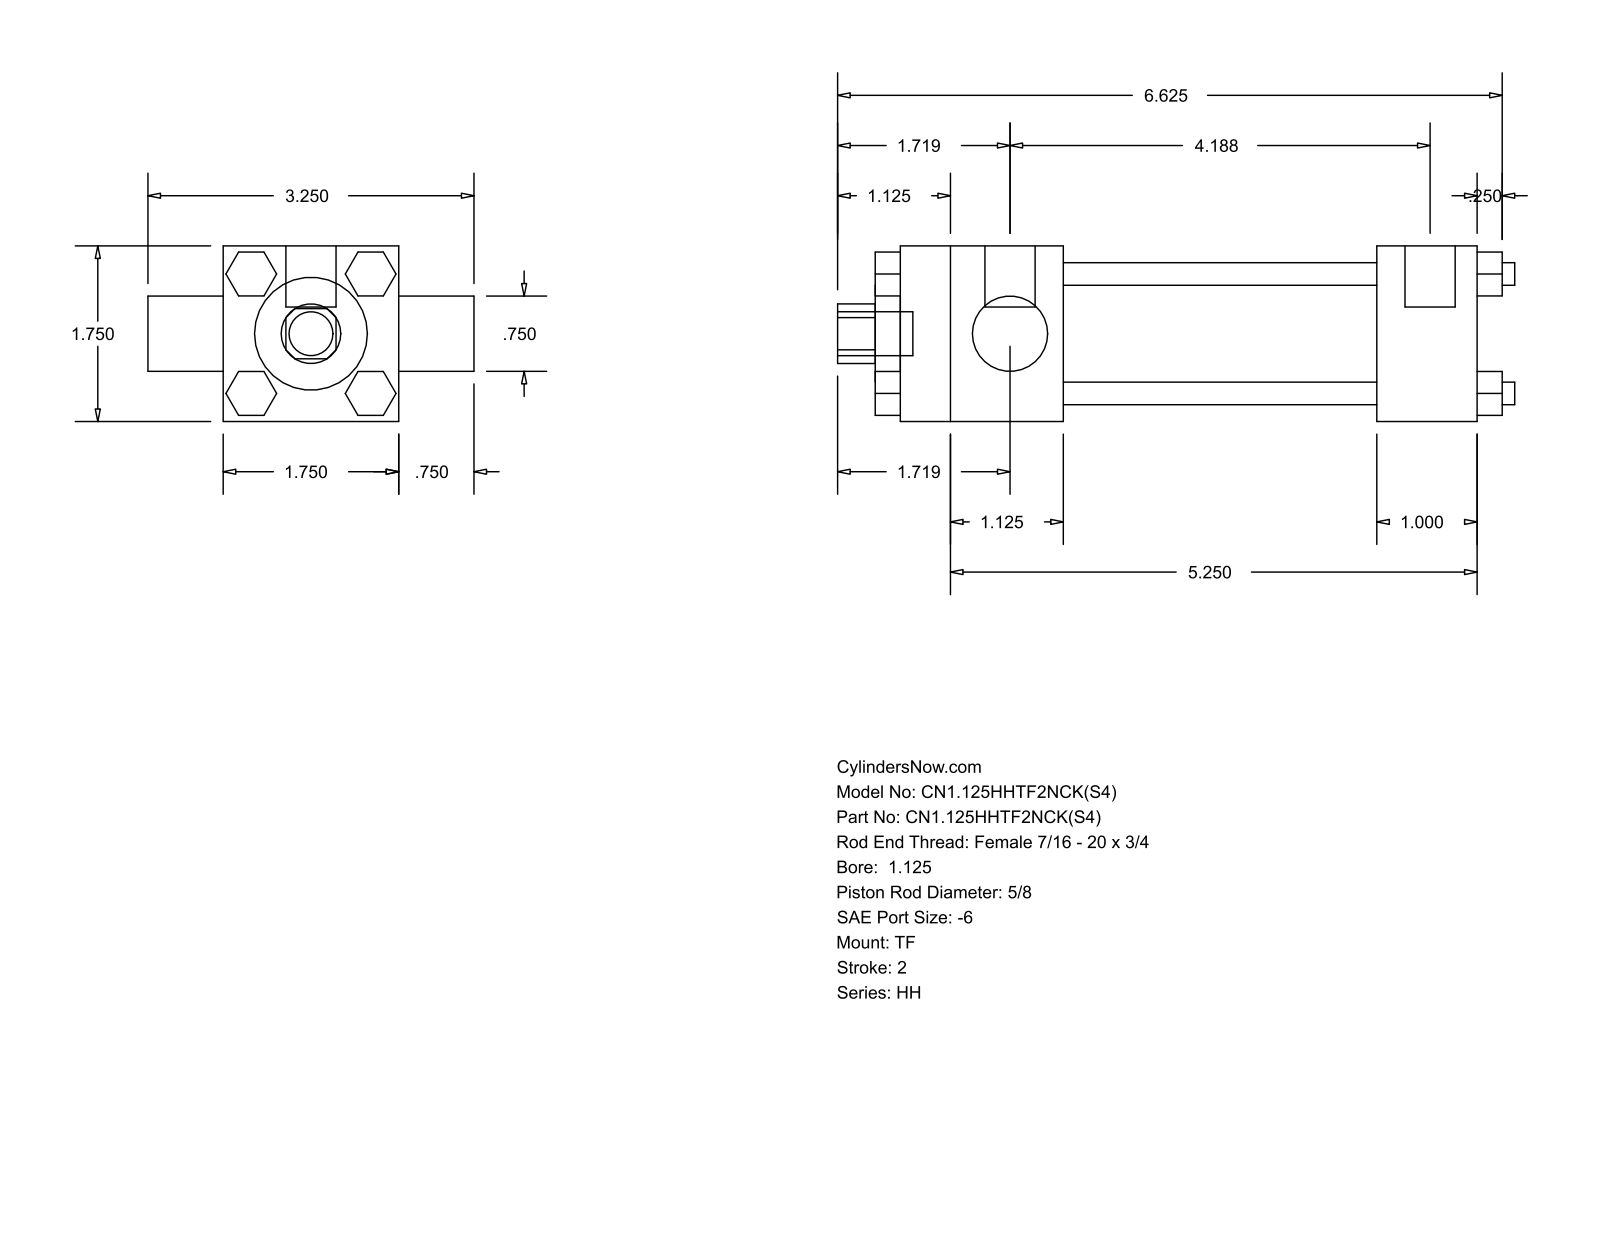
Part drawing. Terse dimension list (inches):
name: HH_TF__0112_0.625
written by: GSSL Pune (CONFIG_CONTROL_DESIGN)
unit: in
bodies: 0 solids, 120 faces (92 planar, 28 cylindrical, 0 other)
size: 6.75 × 3.25 × 1.75
holes: 1× ⌀0.625, 1× ⌀0.75, 1× ⌀1.125, 1× ⌀1.375
bosses: 4× ⌀0.225, 3× ⌀0.219, 2× ⌀0.5, 1× ⌀0.437
rounds: 1× R0.297
face distances: 1.75, 6, 0.25, 0.437, 3.125, 4.125, 1, 1.625, 4.75, 5.75
